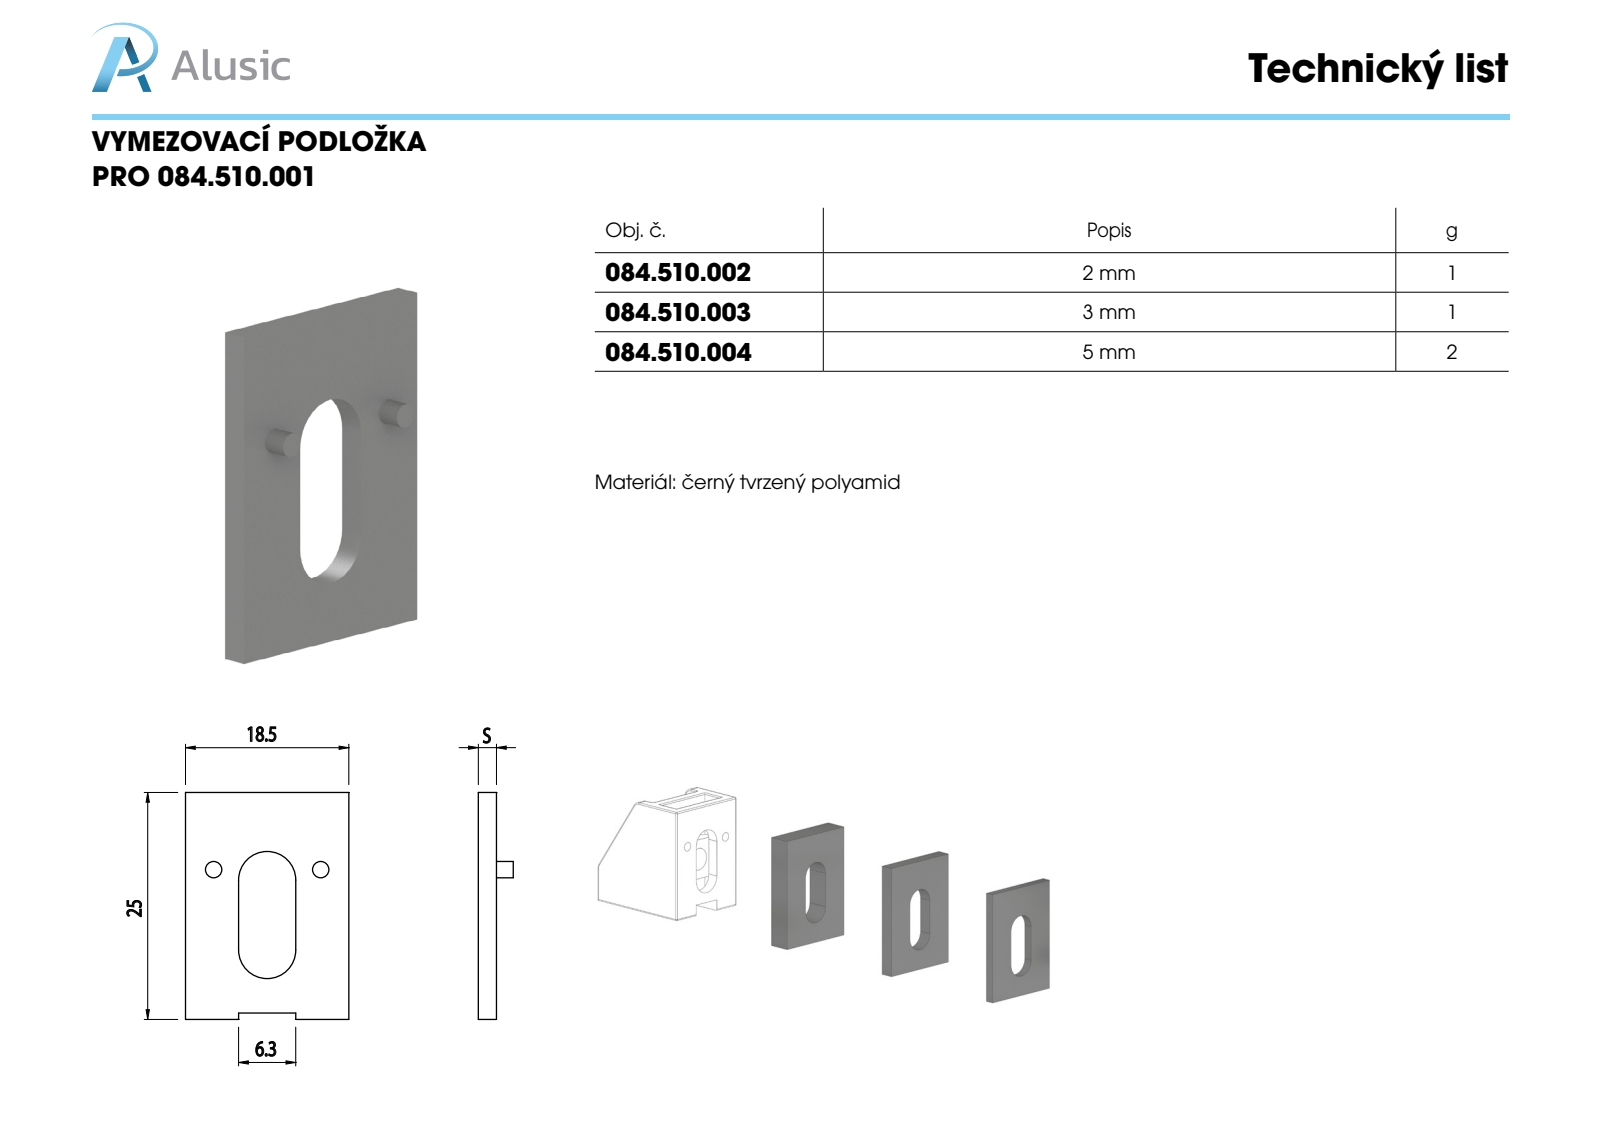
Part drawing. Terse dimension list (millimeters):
name: 084.510.002
written by: SolidWorks 2011 (CONFIG_CONTROL_DESIGN)
unit: mm
bodies: 1 solid, 16 faces (10 planar, 6 cylindrical, 0 other)
size: 25 × 18 × 3.85
volume: 750 mm³; area: 1 004 mm²
bosses: 2× ⌀1.8
rounds: 2× R3.15
face distances: 2, 18, 25, 5.85, 12.15, 6.3, 3.85, 1.85
